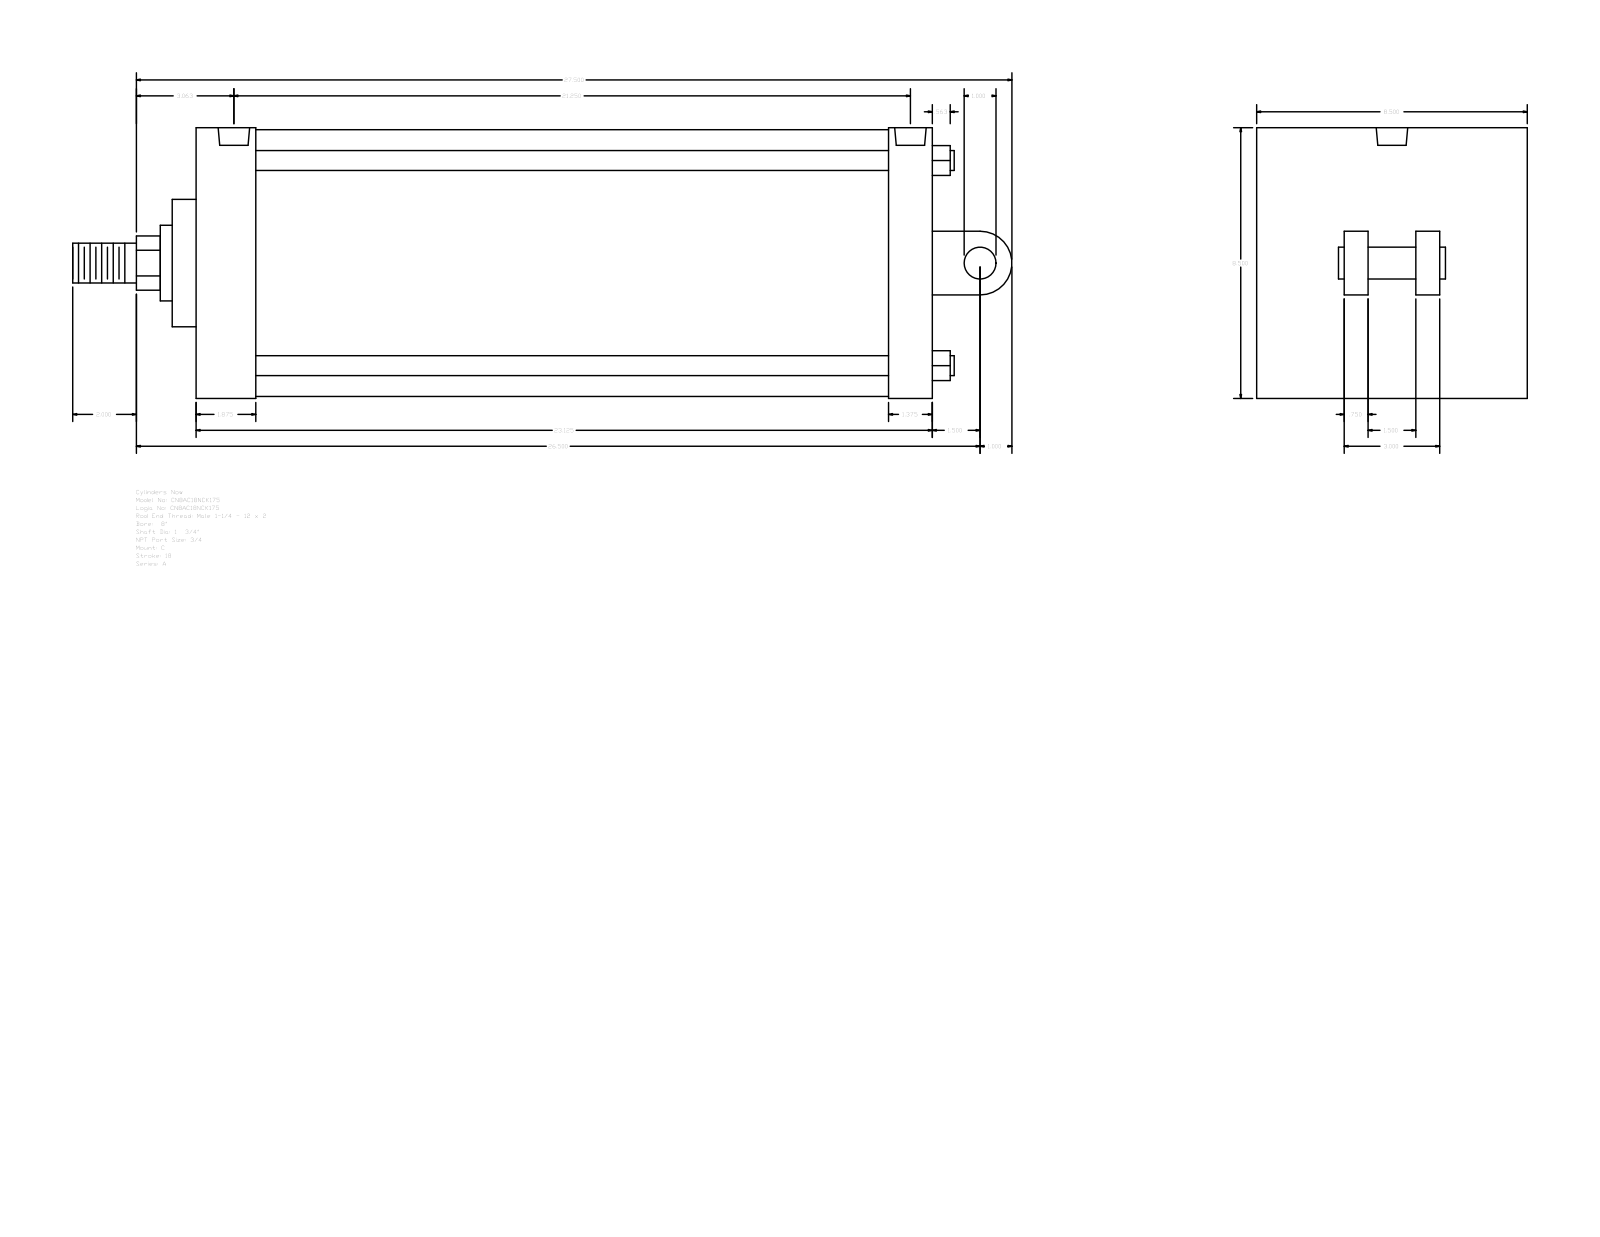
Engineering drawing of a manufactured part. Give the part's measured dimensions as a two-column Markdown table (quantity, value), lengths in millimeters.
| quantity | value |
| --- | --- |
| part name | A_C__0800_1.75 |
| STEP written by | GSSL Pune (CONFIG_CONTROL_DESIGN) |
| units | millimeters |
| bodies | 0 solids, 104 faces (75 planar, 29 cylindrical, 0 other) |
| overall size | 749.3 × 215.9 × 215.9 |
| round holes (diameter × count) | 15.08 × 4, 25.12 × 2 |
| round bosses / shafts (diameter × count) | 15.88 × 4, 212.72 × 1, 60.33 × 1, 44.45 × 1, 31.75 × 1, 25.4 × 1 |
| partial cylindrical surfaces (radius × count) | 21.63 × 1, 25.4 × 1 |
| main face-to-face distances | 587.38, 215.9, 19.05, 57.15, 47.63, 539.75, 552.46, 504.83, 34.92, 69.85 |
| hole center spacings | 6.35, 527.05, 533.4, 539.75 |
